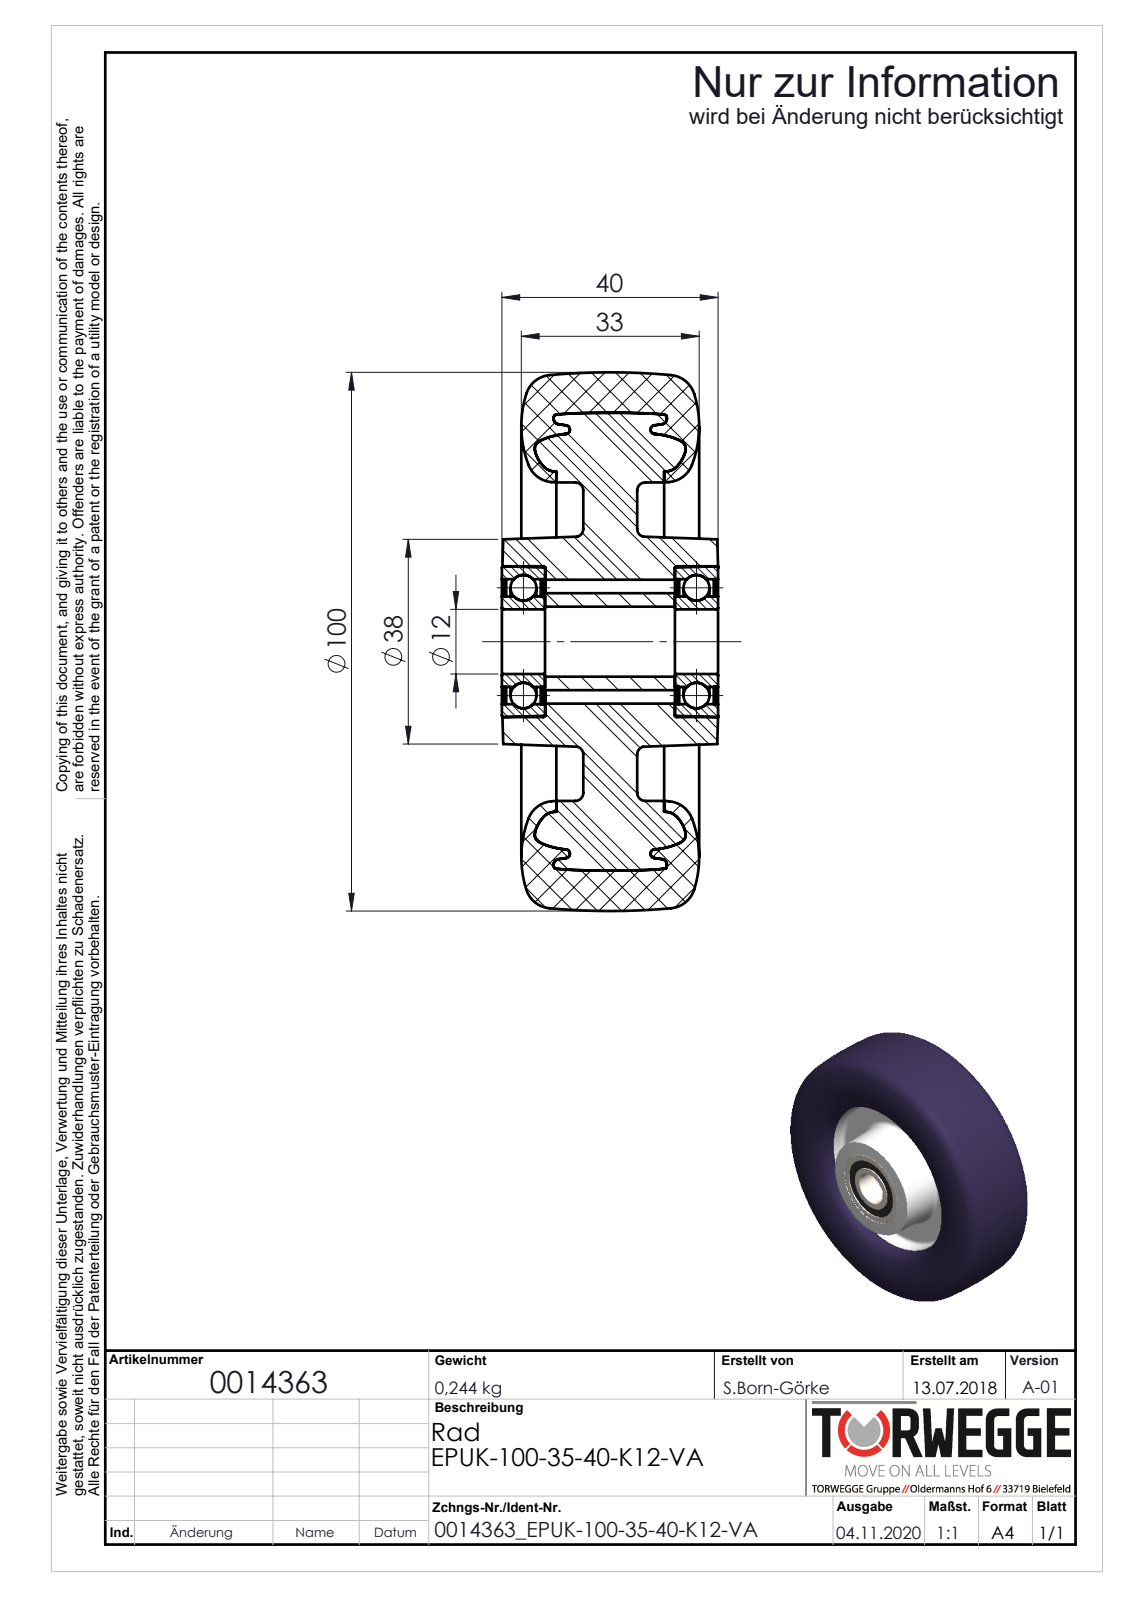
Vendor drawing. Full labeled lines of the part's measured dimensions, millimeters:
Part name (STEP PRODUCT): 0014363
STEP written by: SolidWorks 2018 (AUTOMOTIVE_DESIGN)
Units: millimetres
Bodies: 12 solids, 258 faces (54 planar, 58 cylindrical, 146 other)
Overall size (bounding box): 100 × 100 × 40.1
Volume: 207 977 mm³ · Surface area: 45 283 mm²
Round holes (diameter × count): ⌀12 ×1, ⌀13 ×1, ⌀16.8 ×1, ⌀23 ×1, ⌀23.2 ×1, ⌀59.12 ×1
Round bosses / shafts (diameter × count): ⌀28 ×1, ⌀18 ×1
Partial cylindrical surfaces — rounded edges, fillets, slot ends (radius × count): R39.5 ×1
Main face-to-face distances: 32.1, 10, 7.2, 7.7, 0.8, 0.5, 6.9, 7, 17, 7.4
